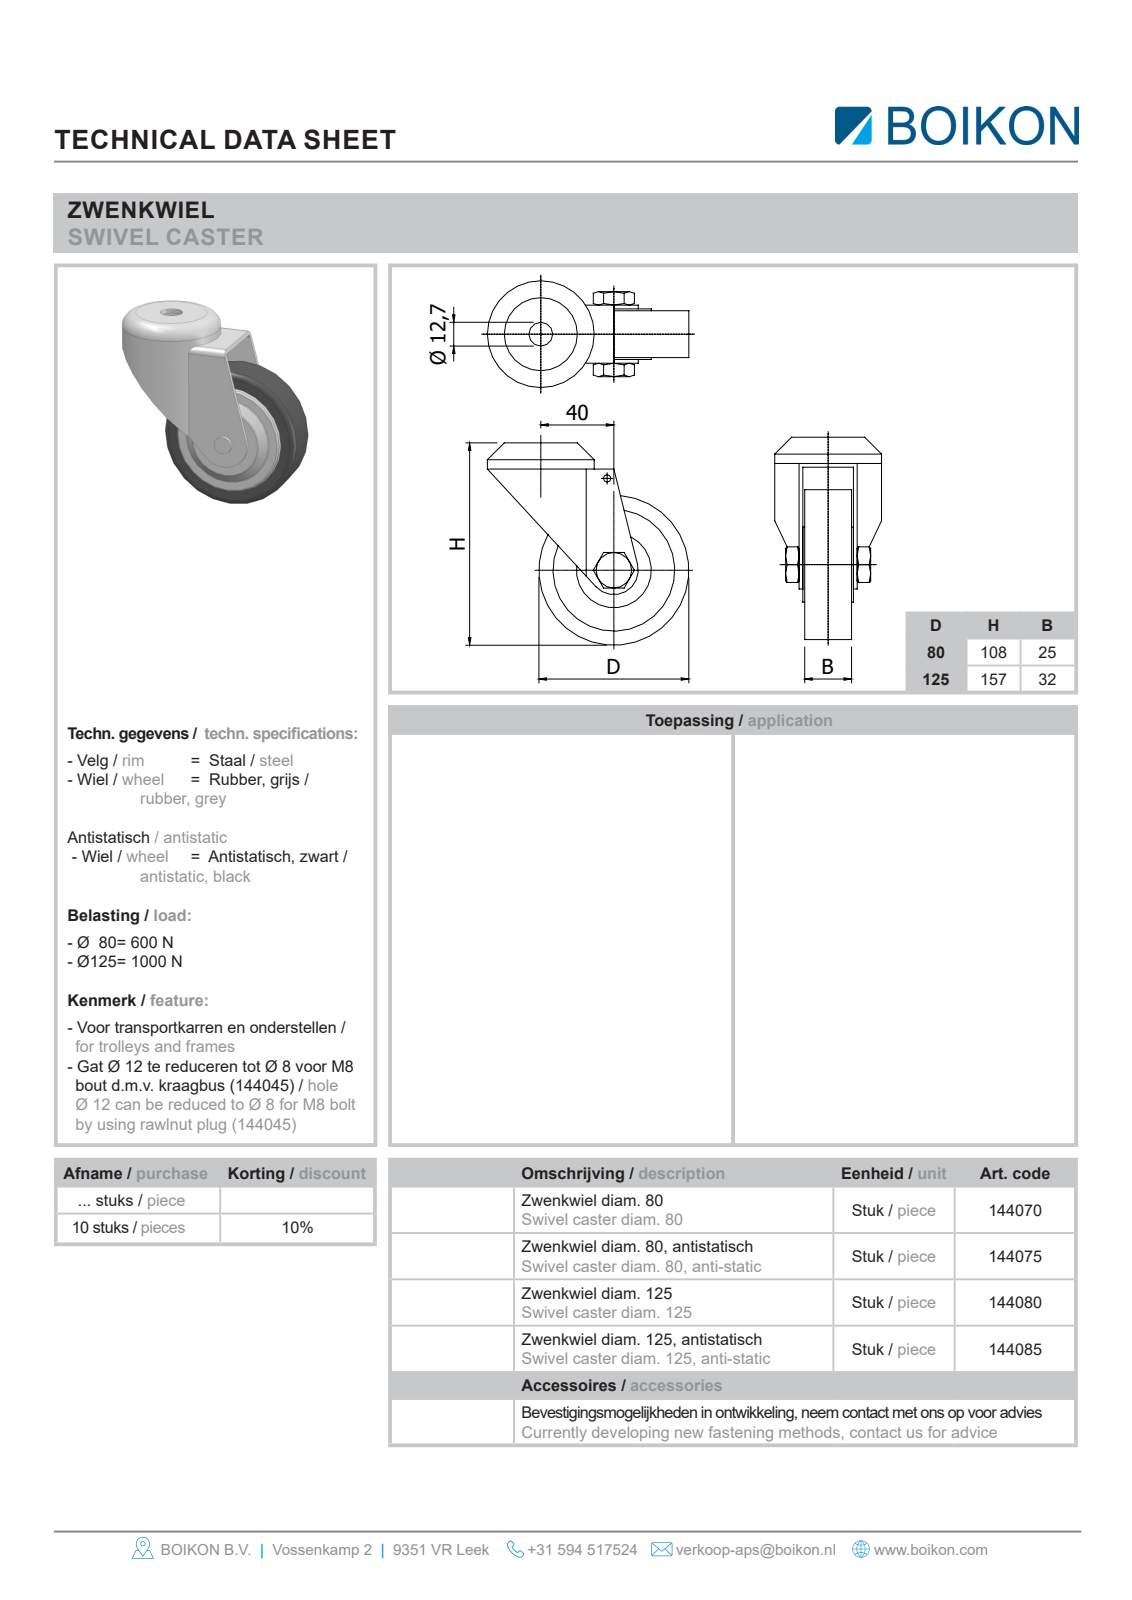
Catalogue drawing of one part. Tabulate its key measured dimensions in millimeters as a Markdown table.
| quantity | value |
| --- | --- |
| part name | Root; 144075Zwenkwiel diam. 80 antistatischBOIKON |
| STEP written by | HiCAD 2013 1802.4 Build 509 (AUTOMOTIVE_DESIGN) |
| units | millimeters |
| bodies | 1 solid, 47 faces (18 planar, 15 cylindrical, 14 other) |
| overall size | 108.5 × 108 × 57 |
| volume | 180 481 mm³ |
| surface area | 38 328 mm² |
| round holes (diameter × count) | 13 × 1, 52 × 1 |
| round bosses / shafts (diameter × count) | 80 × 1, 62 × 1, 57 × 1, 10 × 1 |
| partial cylindrical surfaces (radius × count) | 1.5 × 2, 4 × 2, 14 × 1 |
| main face-to-face distances | 2.5, 40.5, 33.75, 6.75, 34.25, 6.25, 43, 27.5, 6.5, 31.5 |
